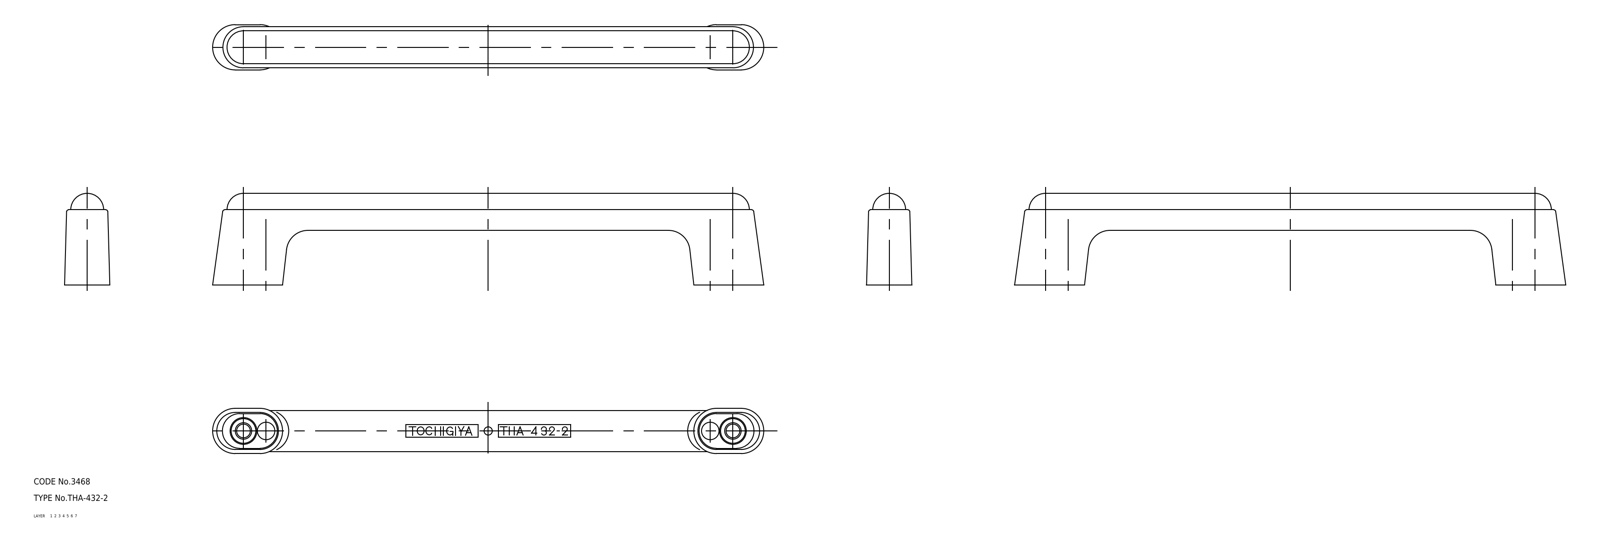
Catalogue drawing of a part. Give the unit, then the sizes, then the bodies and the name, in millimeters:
Units: millimetres
Overall size (bounding box): 268 × 44.5 × 22
Volume: 53 150 mm³ · Surface area: 45 345 mm²
Bodies: 2 solids, 127 faces (0 planar, 0 cylindrical, 127 other)
Part name (STEP PRODUCT): pull; cover; THA_432_2_235_36
STEP written by: CADfix (AUTOMOTIVE_DESIGN)
